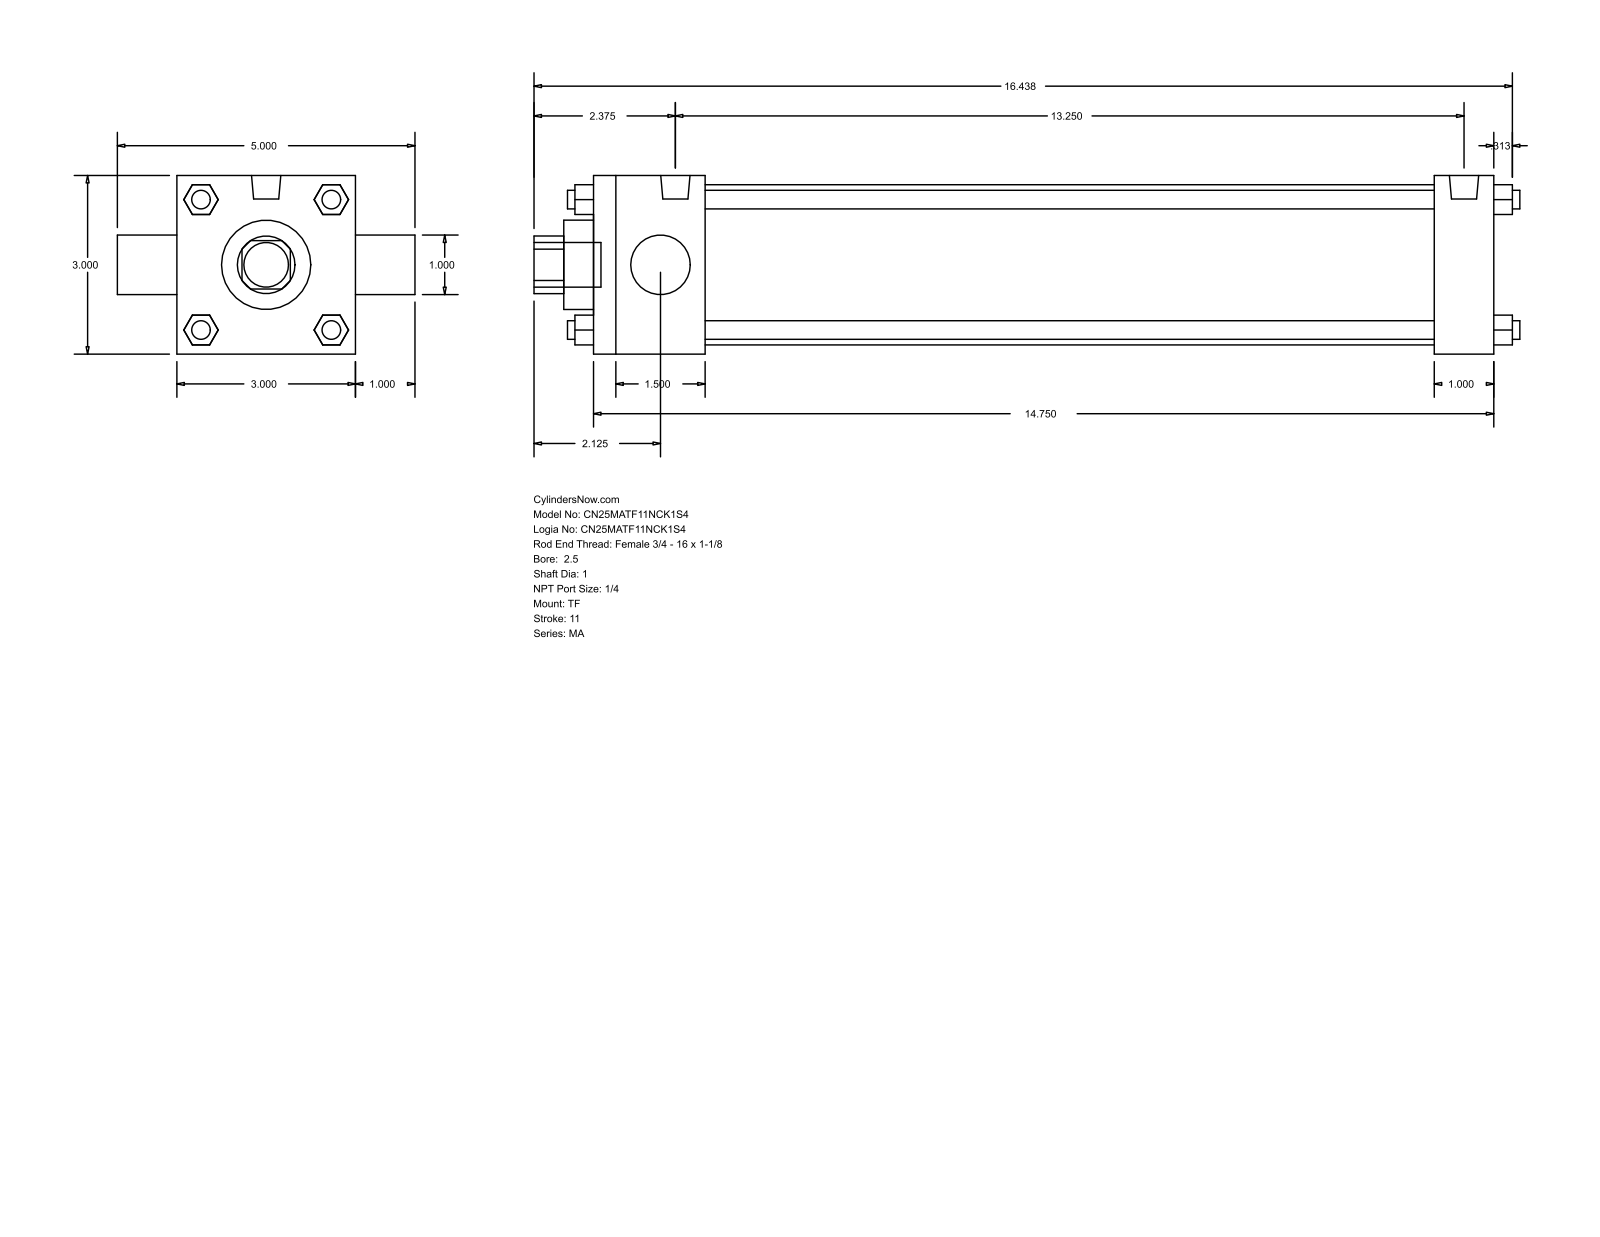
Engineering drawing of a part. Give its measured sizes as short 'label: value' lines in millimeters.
name: MA_TF__0250_1
written by: GSSL Pune (CONFIG_CONTROL_DESIGN)
unit: mm
bodies: 0 solids, 120 faces (92 planar, 28 cylindrical, 0 other)
size: 420.69 × 127 × 76.2
holes: 2× ⌀25.4, 1× ⌀38.1, 1× ⌀68.33
bosses: 7× ⌀7.94, 2× ⌀12.49, 1× ⌀19.05
rounds: 1× R12.29
face distances: 76.2, 384.17, 12.7, 47.63, 358.78, 311.15, 336.54, 25.39, 25.4, 101.6
